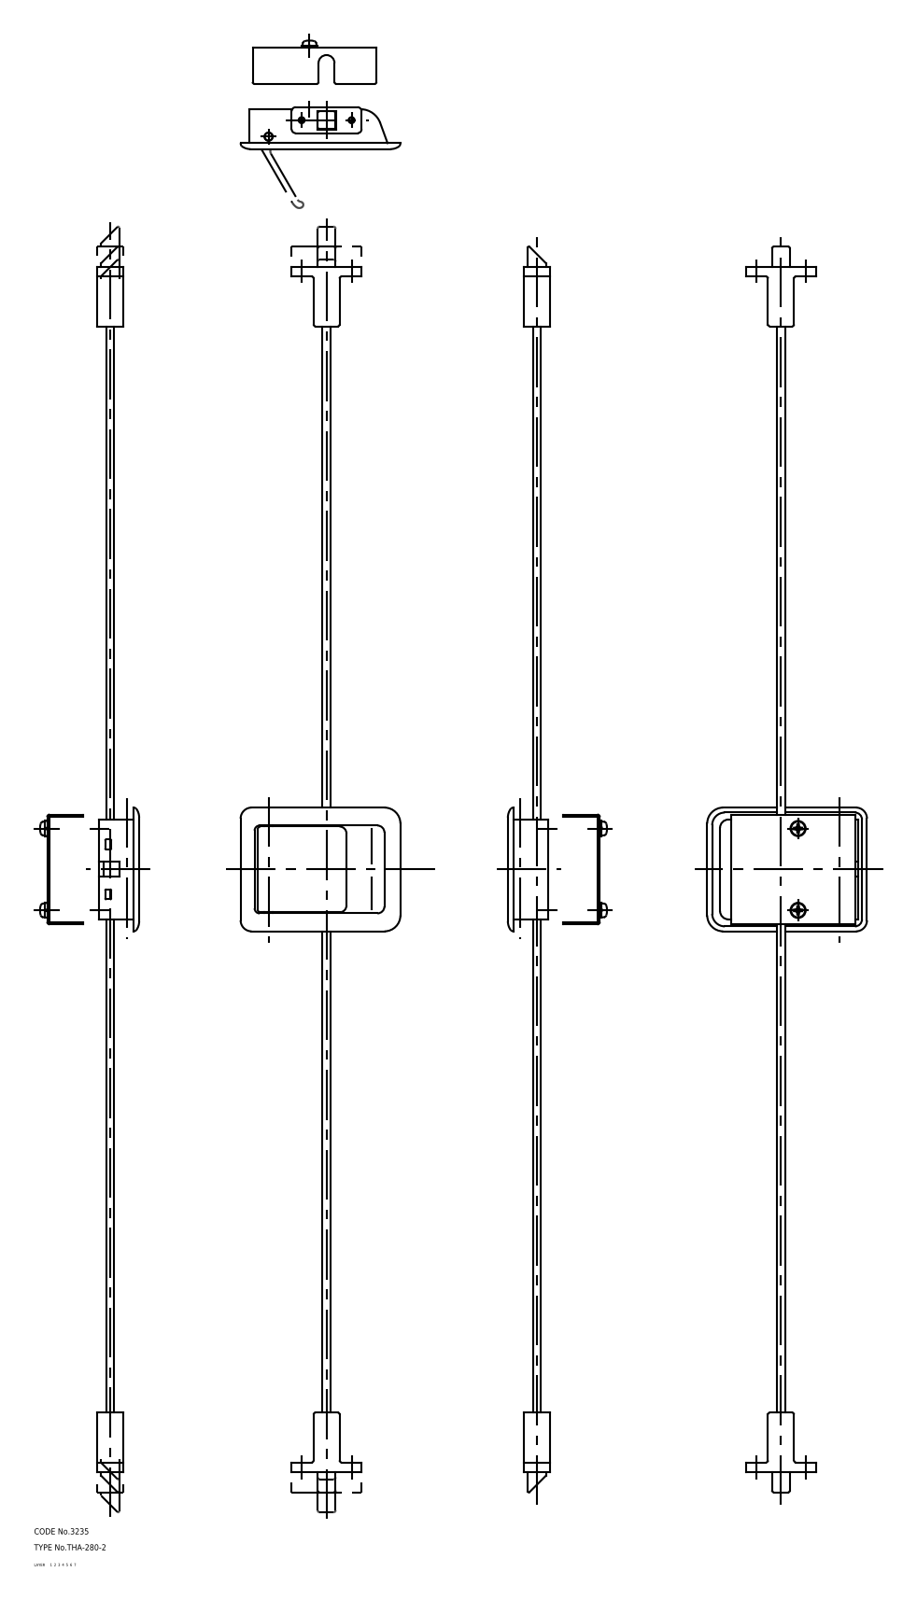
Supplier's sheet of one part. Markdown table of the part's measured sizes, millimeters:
| quantity | value |
| --- | --- |
| part name | screw; shaft; rod_A_mr; rod_A (+8 more) |
| STEP written by | CADfix (AUTOMOTIVE_DESIGN) |
| units | millimeters |
| bodies | 13 solids, 394 faces (0 planar, 0 cylindrical, 394 other) |
| overall size | 624 × 80 × 27.05 |
| volume | 68 705 mm³ |
| surface area | 55 290 mm² |
